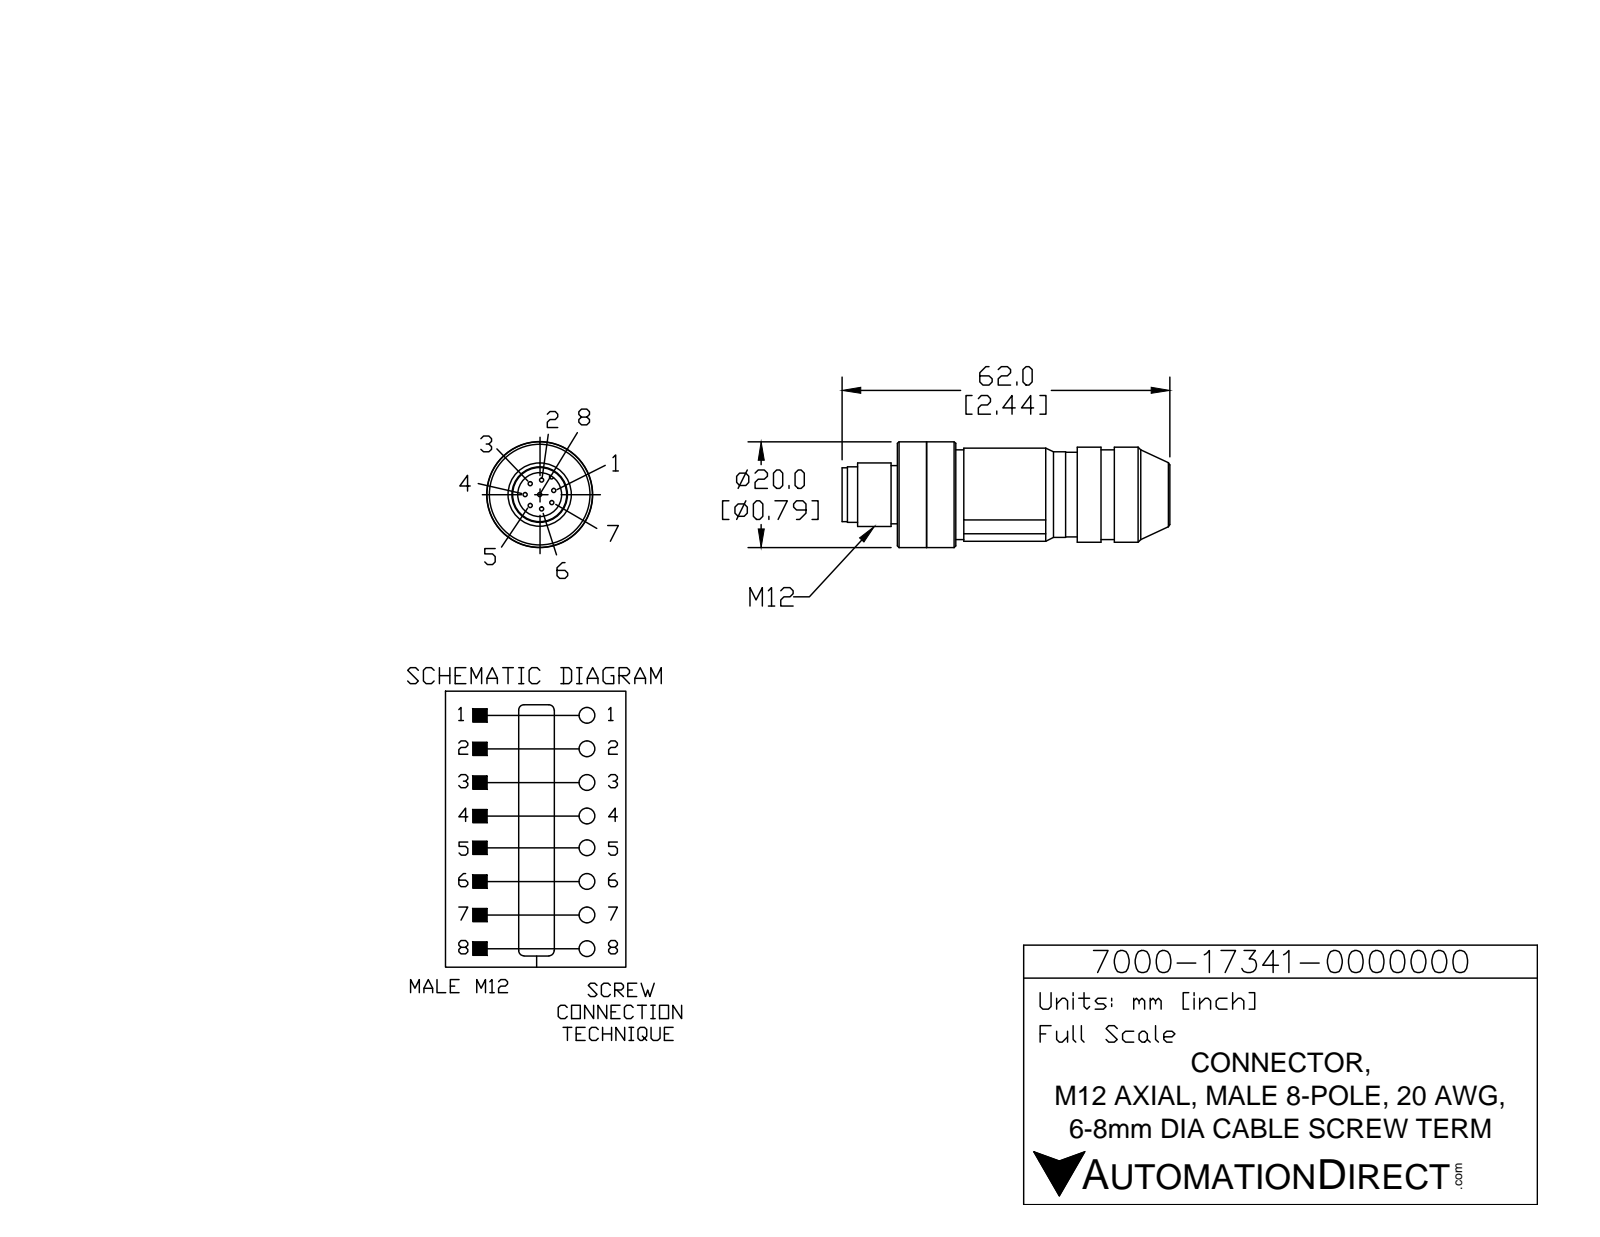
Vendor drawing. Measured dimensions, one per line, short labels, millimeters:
name: 7000-17341-0000000
written by: SolidWorks 2015 (AUTOMOTIVE_DESIGN)
unit: mm
bodies: 2 solids, 96 faces (24 planar, 50 cylindrical, 22 other)
size: 62 × 20 × 20
volume: 13 069 mm³; area: 5 139 mm²
holes: 1× ⌀4.5, 1× ⌀8.2
bosses: 8× ⌀0.8, 1× ⌀20, 1× ⌀18, 1× ⌀17.6, 1× ⌀17, 1× ⌀16.2, 1× ⌀16, 1× ⌀12
rounds: 1× R0.6
face distances: 5.5, 5.55, 7, 35.55, 23, 28.5, 11.05, 1.5, 7.05, 12.55
